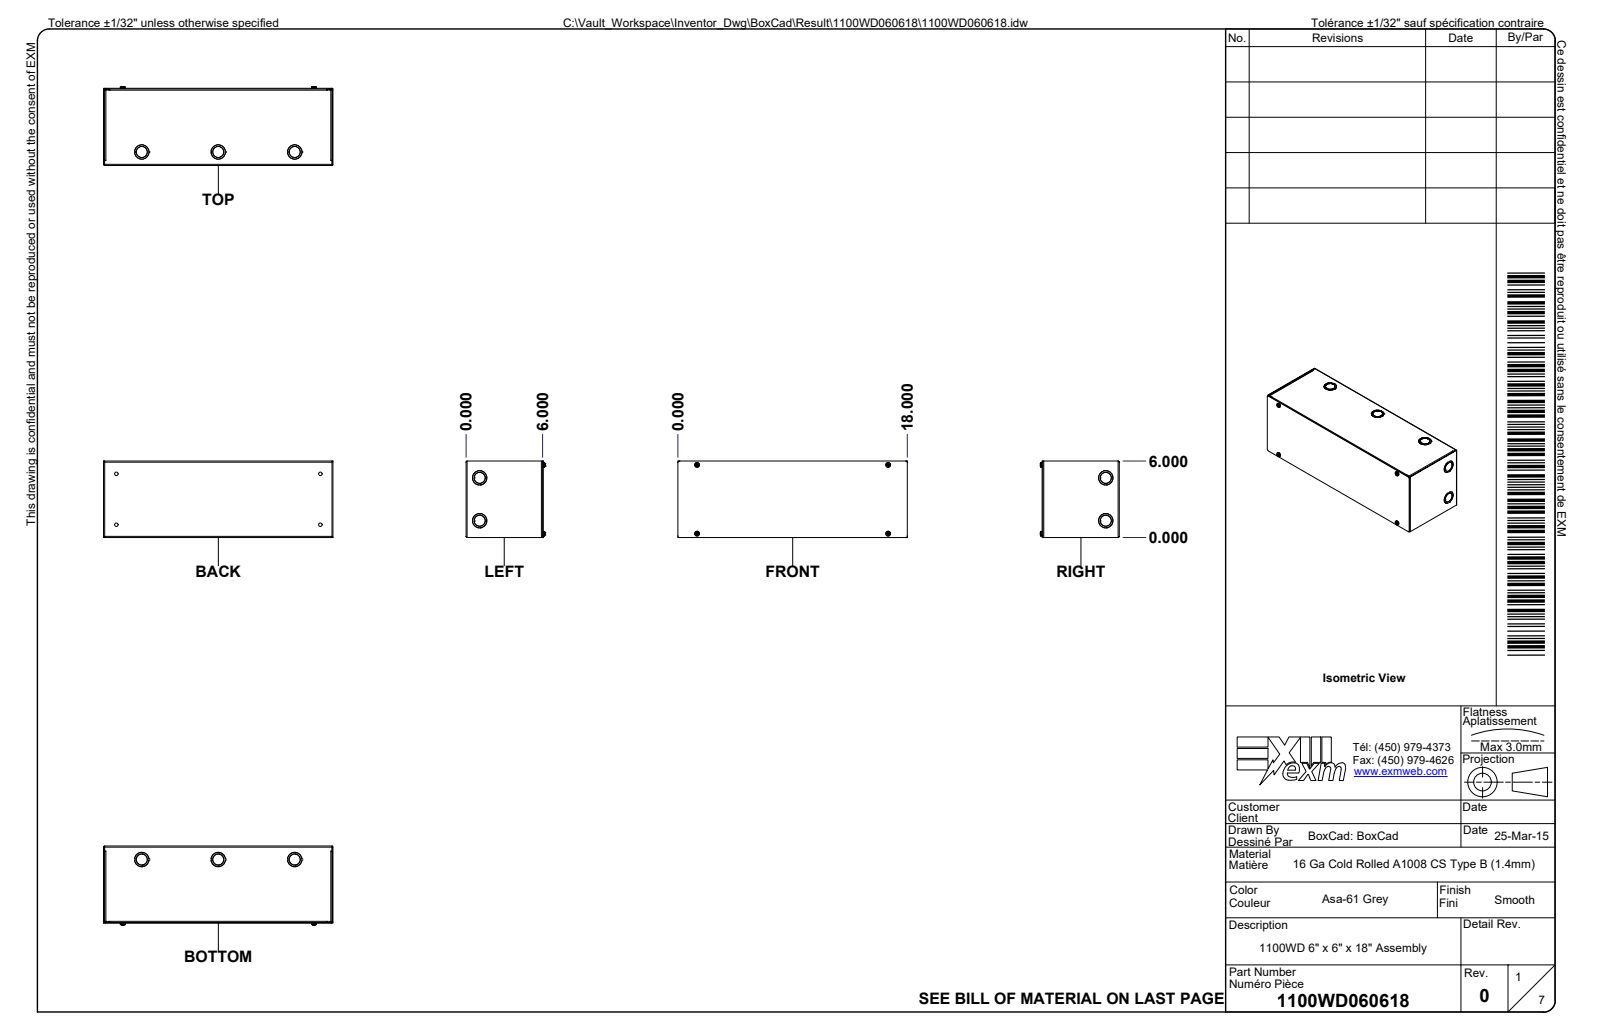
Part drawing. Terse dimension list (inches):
name: 1100WD060618; 1100WD060618B; 1100WD060618B-P; 1100WD060618C (+5 more)
written by: Autodesk Inventor 2024 (AUTOMOTIVE_DESIGN)
unit: in
bodies: 8 solids, 3381 faces (2062 planar, 427 cylindrical, 892 other)
size: 18 × 6.183 × 6
volume: 28.95 in³; area: 1 080 in²
holes: 8× ⌀0.29, 5× ⌀0.875, 5× ⌀1.125, 4× ⌀0.165, 2× ⌀0.033, 2× ⌀0.177, 1× ⌀0.043, 1× ⌀0.312, 1× ⌀1.063
bosses: 5× ⌀1.125, 5× ⌀0.875, 4× ⌀0.374, 2× ⌀0.03, 1× ⌀1.25, 1× ⌀1.142, 1× ⌀0.25, 1× ⌀0.051
rounds: 28× R0.004, 14× R0.031, 14× R0.086, 12× R0.059, 12× R0.11, 4× R0.062, 4× R0.094, 4× R0.125
face distances: 0.055, 5.945, 6, 5.89, 0.053, 6.053, 5.998, 17.945, 18, 17.89
hole spacings: 0.86, 4.726, 15.516, 16.197, 8.681, 4, 4.625, 5.4
